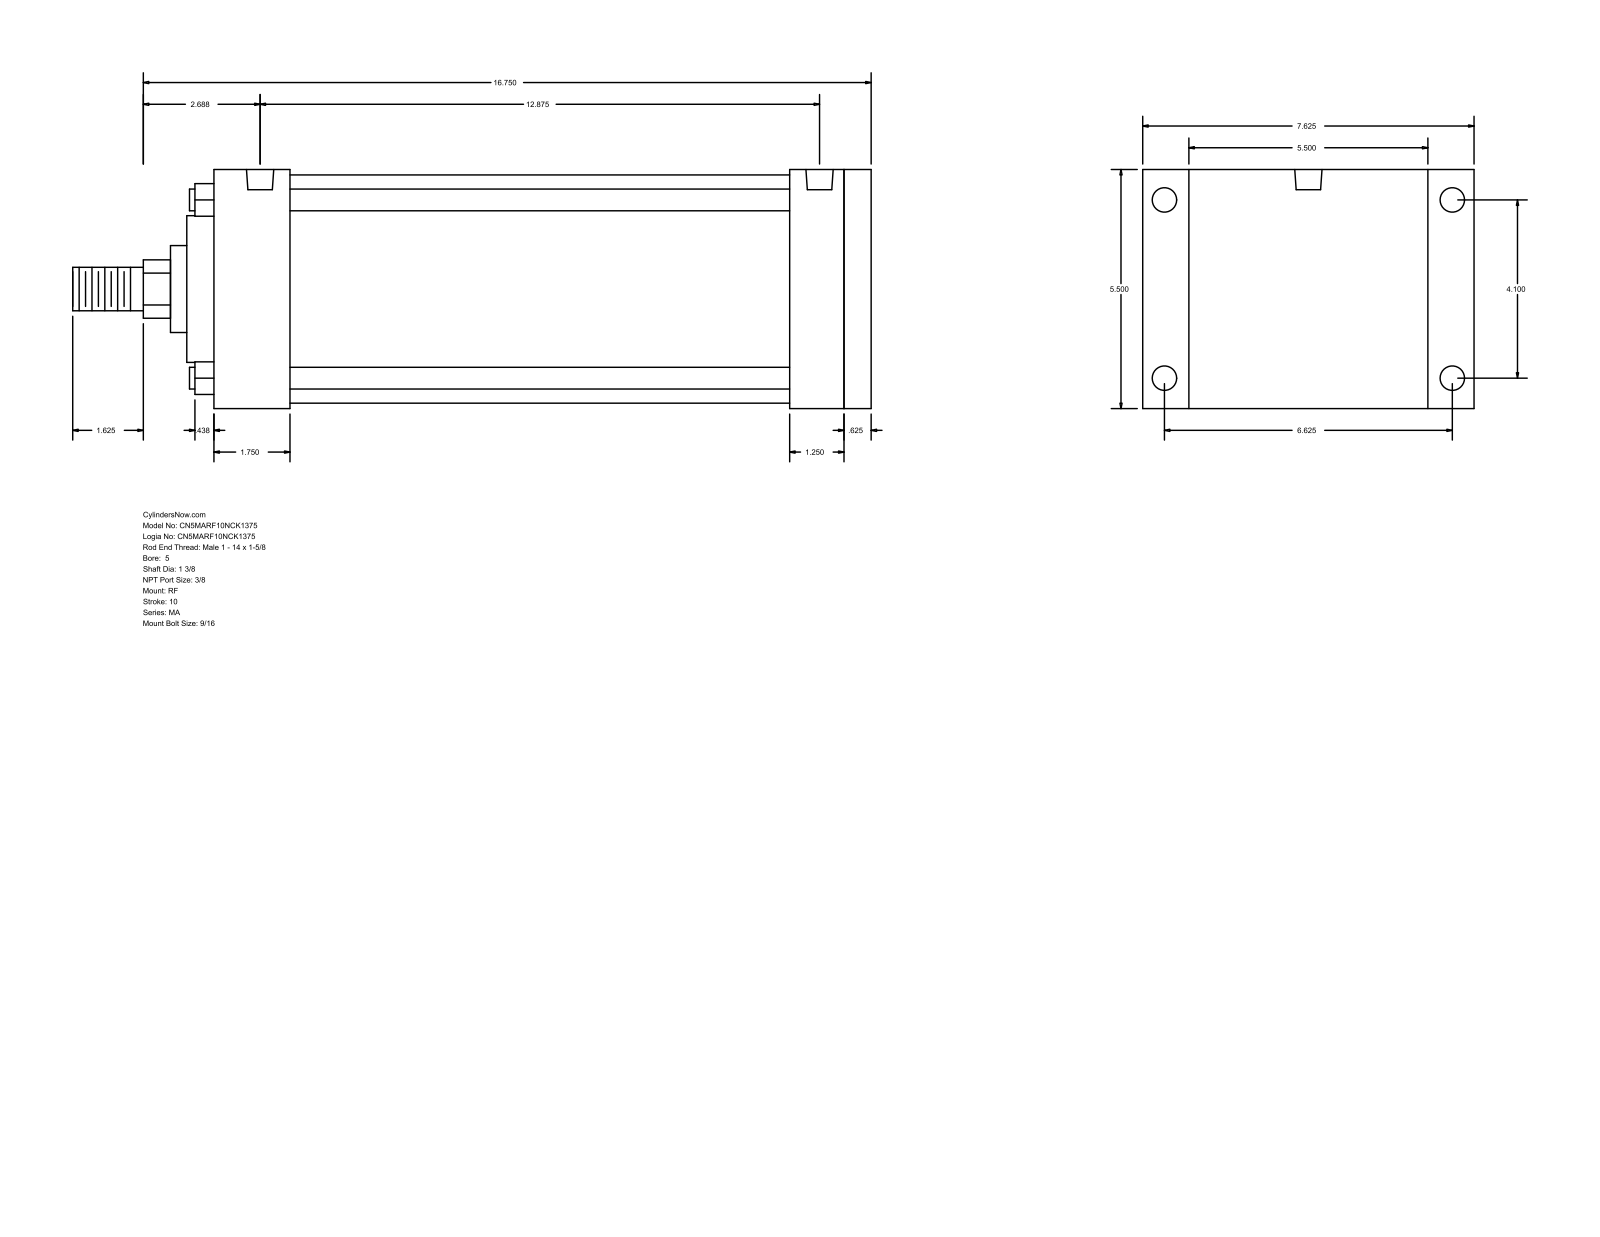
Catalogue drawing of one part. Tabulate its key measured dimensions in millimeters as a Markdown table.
| quantity | value |
| --- | --- |
| part name | MA_RF__0500_1.375 |
| STEP written by | GSSL Pune (CONFIG_CONTROL_DESIGN) |
| units | millimeters |
| bodies | 0 solids, 94 faces (65 planar, 29 cylindrical, 0 other) |
| overall size | 466.73 × 193.68 × 139.7 |
| round holes (diameter × count) | 11.11 × 4, 14.29 × 4, 15.93 × 2 |
| round bosses / shafts (diameter × count) | 12.7 × 4, 133.35 × 1, 85.72 × 1, 50.8 × 1, 34.92 × 1, 25.4 × 1 |
| partial cylindrical surfaces (radius × count) | 17.06 × 1 |
| main face-to-face distances | 139.7, 384.18, 15.88, 368.3, 44.45, 323.85, 339.73, 336.55, 292.1, 31.75 |
| hole center spacings | 4.77, 104.14, 168.28, 197.9, 317.49, 322.26, 327.03 |
